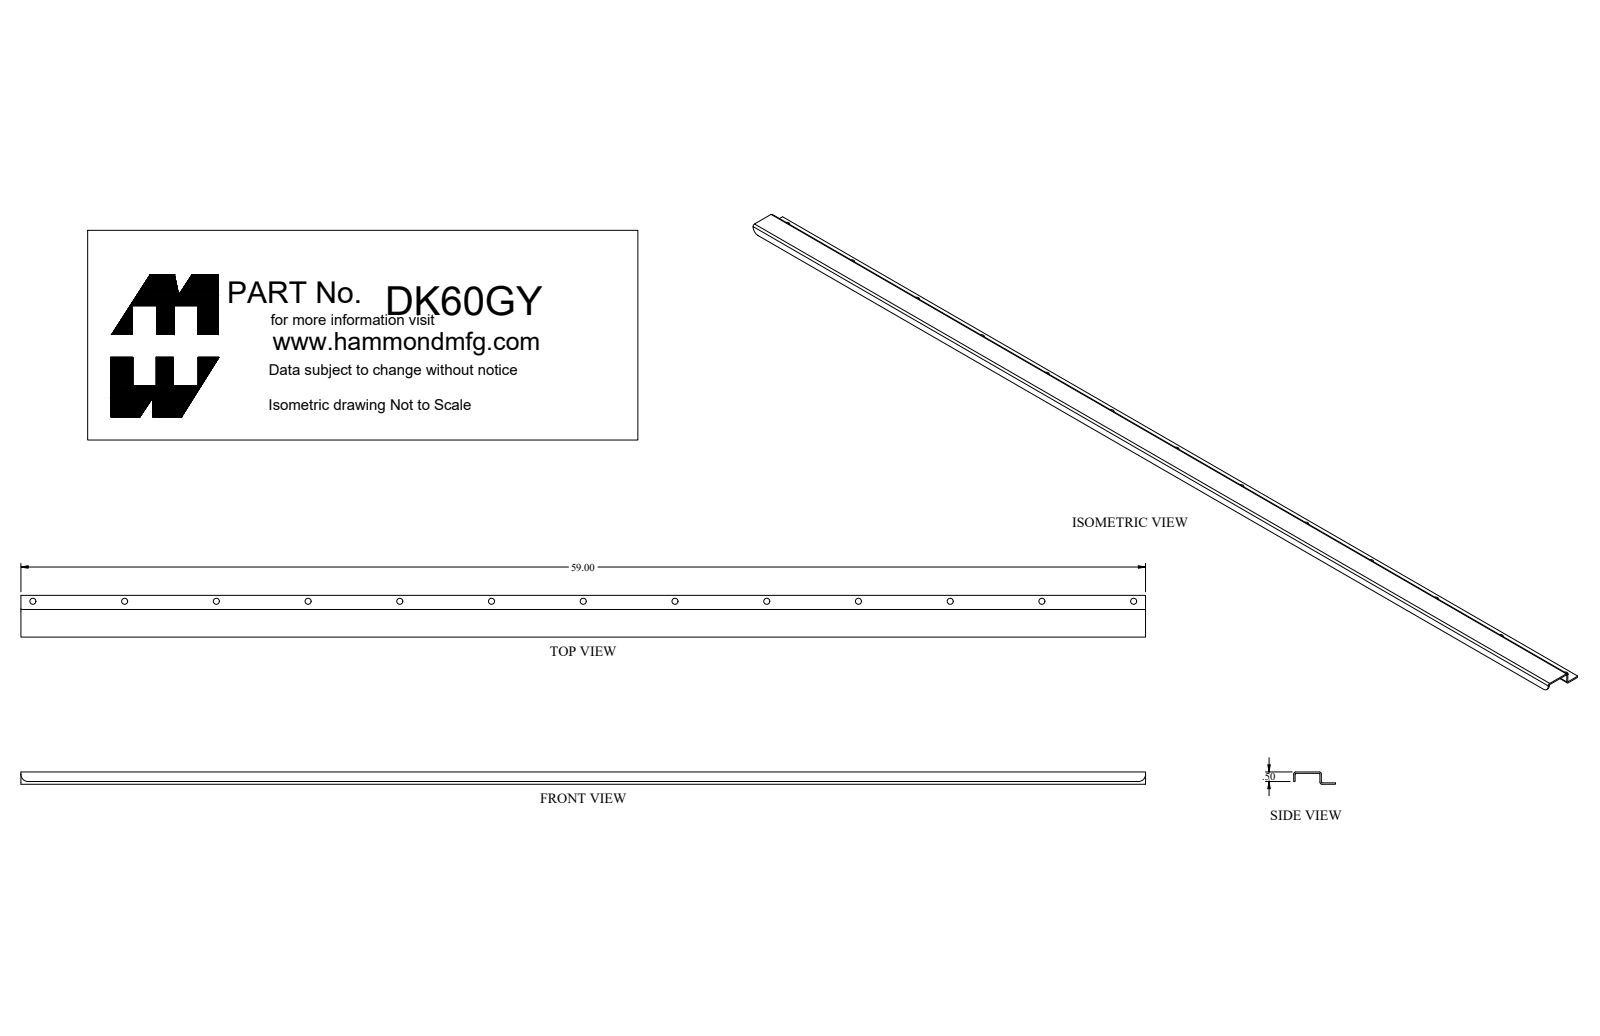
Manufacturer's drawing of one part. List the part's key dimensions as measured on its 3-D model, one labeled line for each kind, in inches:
Part name (STEP PRODUCT): DK60GY_Default
STEP written by: SolidWorks 2018 (CONFIG_CONTROL_DESIGN)
Units: inches
Bodies: 5 solids, 85 faces (35 planar, 44 cylindrical, 6 other)
Overall size (bounding box): 59 × 2.188 × 1.322
Volume: 15.97 in³ · Surface area: 471.7 in²
Round holes (diameter × count): ⌀0.313 ×13, ⌀0.201 ×1, ⌀0.275 ×1
Round bosses / shafts (diameter × count): ⌀0.625 ×1, ⌀0.483 ×1, ⌀0.25 ×1
Partial cylindrical surfaces — rounded edges, fillets, slot ends (radius × count): R0.036 ×3, R0.108 ×3, R0.375 ×2
Main face-to-face distances: 0.072, 0.572, 0.644, 1.376, 0.5, 0.063, 0.635, 0.707, 0.135, 1.448
Hole centre spacings: 4.813, 14.437, 19.25, 9.625, 33.687, 9.625, 28.875, 4.812
